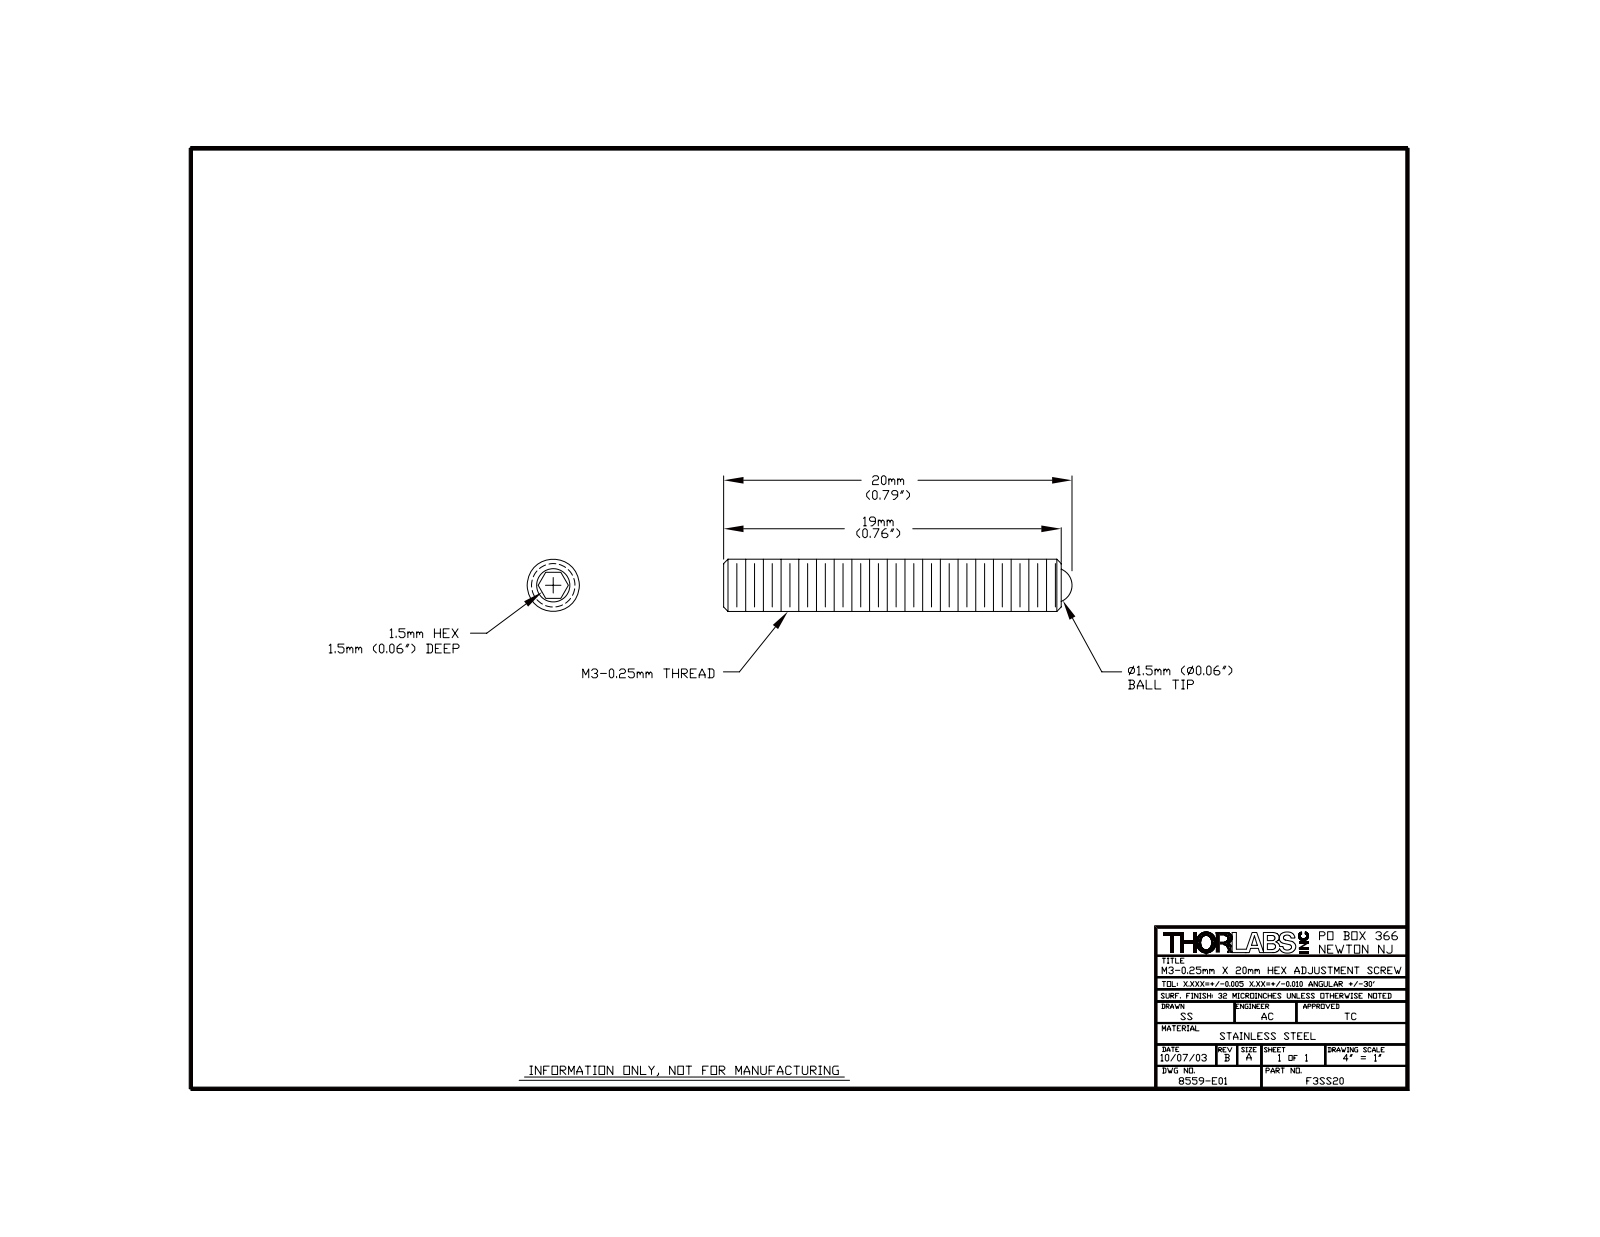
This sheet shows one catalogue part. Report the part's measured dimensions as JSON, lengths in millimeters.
{"part_name": "8559-E0W", "step_written_by": "SolidWorks 2011 (AUTOMOTIVE_DESIGN)", "units": "millimeters", "bodies": {"solids": 2, "faces": 23, "planar": 9, "cylindrical": 4, "other": 10}, "overall_size": [20, 3, 3], "volume_mm3": 100, "surface_area_mm2": 217, "round_holes": [[1.6, 1]], "round_bosses_or_shafts": [[3, 1]], "face_to_face_distances": [1.3, 1.3, 19.3, 3, 16.3]}
